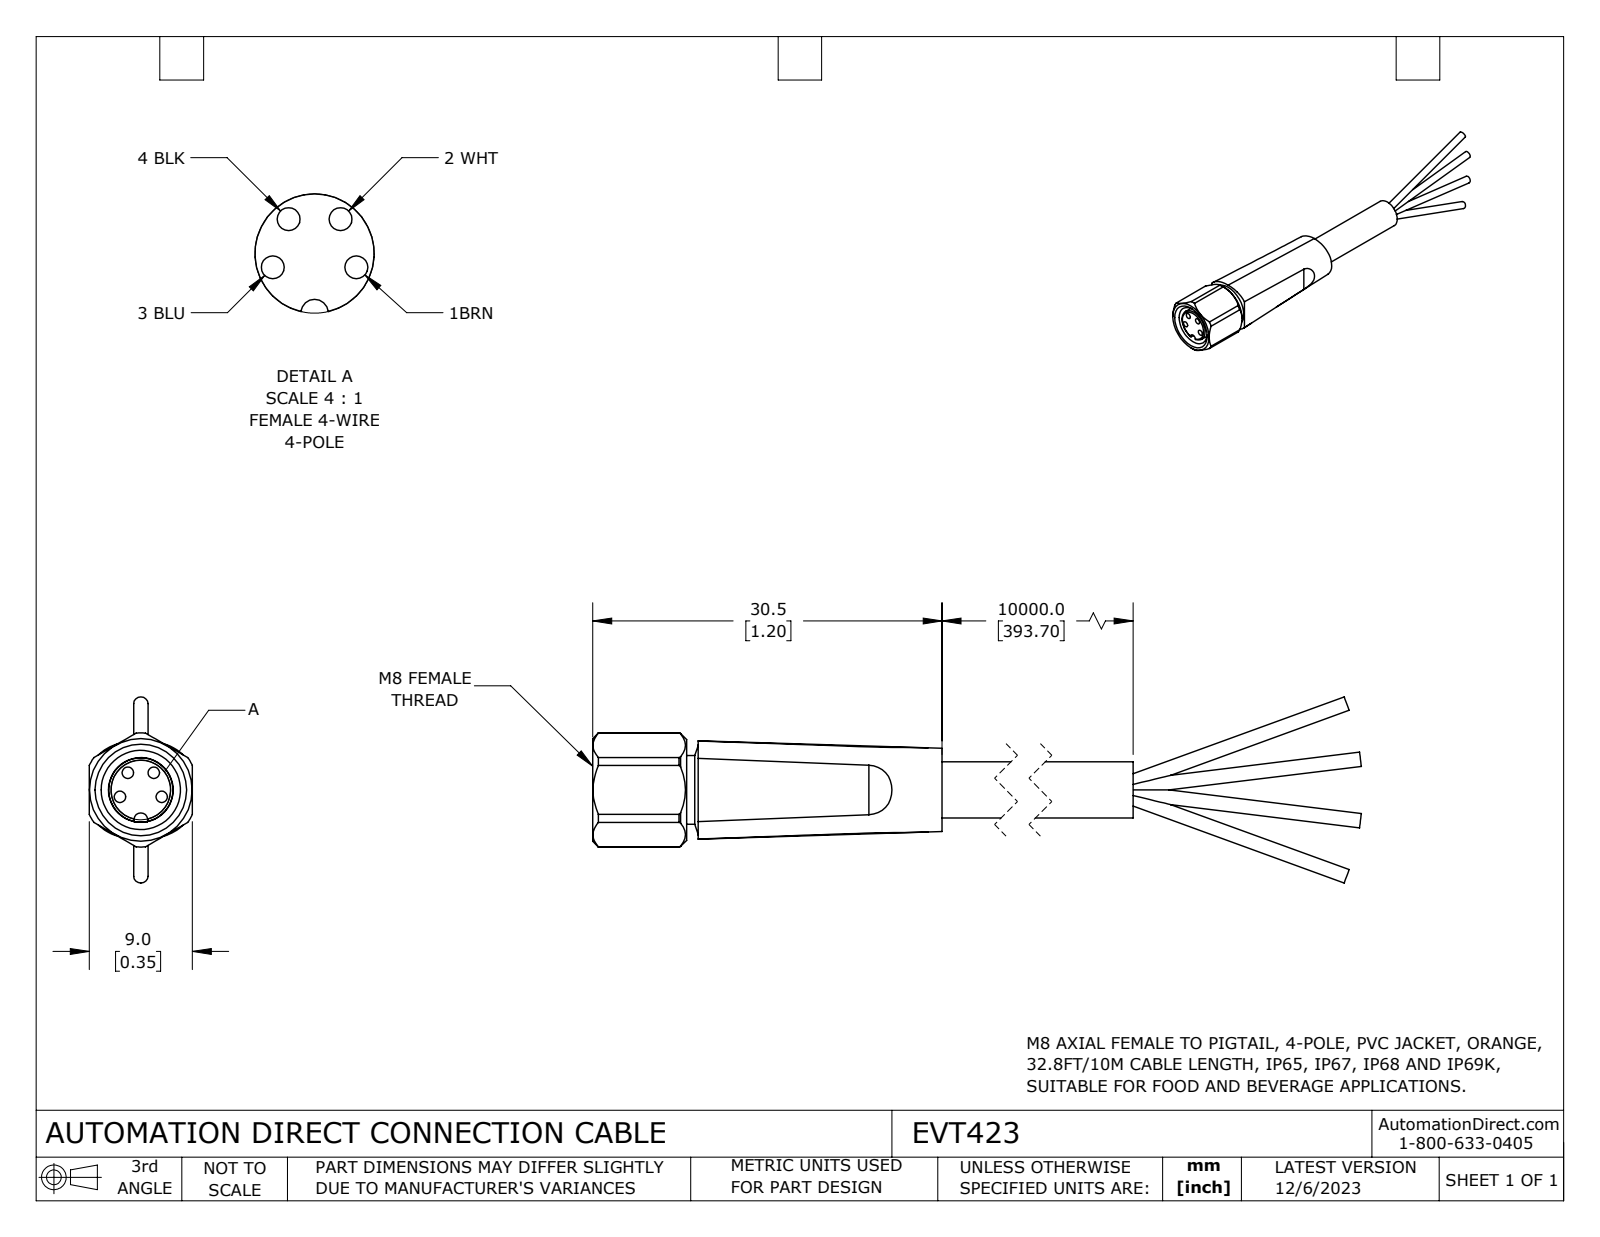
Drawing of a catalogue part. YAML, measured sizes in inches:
part_name: "EVT423"
step_written_by: "SolidWorks 2023 (CONFIG_CONTROL_DESIGN)"
units: inches
bodies: {solids: 1, faces: 82, planar: 26, cylindrical: 35, other: 21}
overall_size: [2.694, 0.64, 0.354]
volume: 0.126
surface_area: 3.03
round_holes:
  - {diameter: 0.039, count: 4}
  - {diameter: 0.272, count: 1}
round_bosses_or_shafts:
  - {diameter: 0.049, count: 4}
  - {diameter: 0.236, count: 1}
  - {diameter: 0.222, count: 1}
  - {diameter: 0.193, count: 1}
partial_cylinders:
  - {radius: 0.133, count: 2}
  - {radius: 0.024, count: 1}
  - {radius: 0.196, count: 1}
face_to_face_distances: [0.354, 0.878, 0.303, 1.181, 1.89, 1.587, 0.709, 0.272, 0.031, 0.909]
hole_center_spacings: [0.074, 0.076, 0.087, 0.143, 0.089, 0.143]
